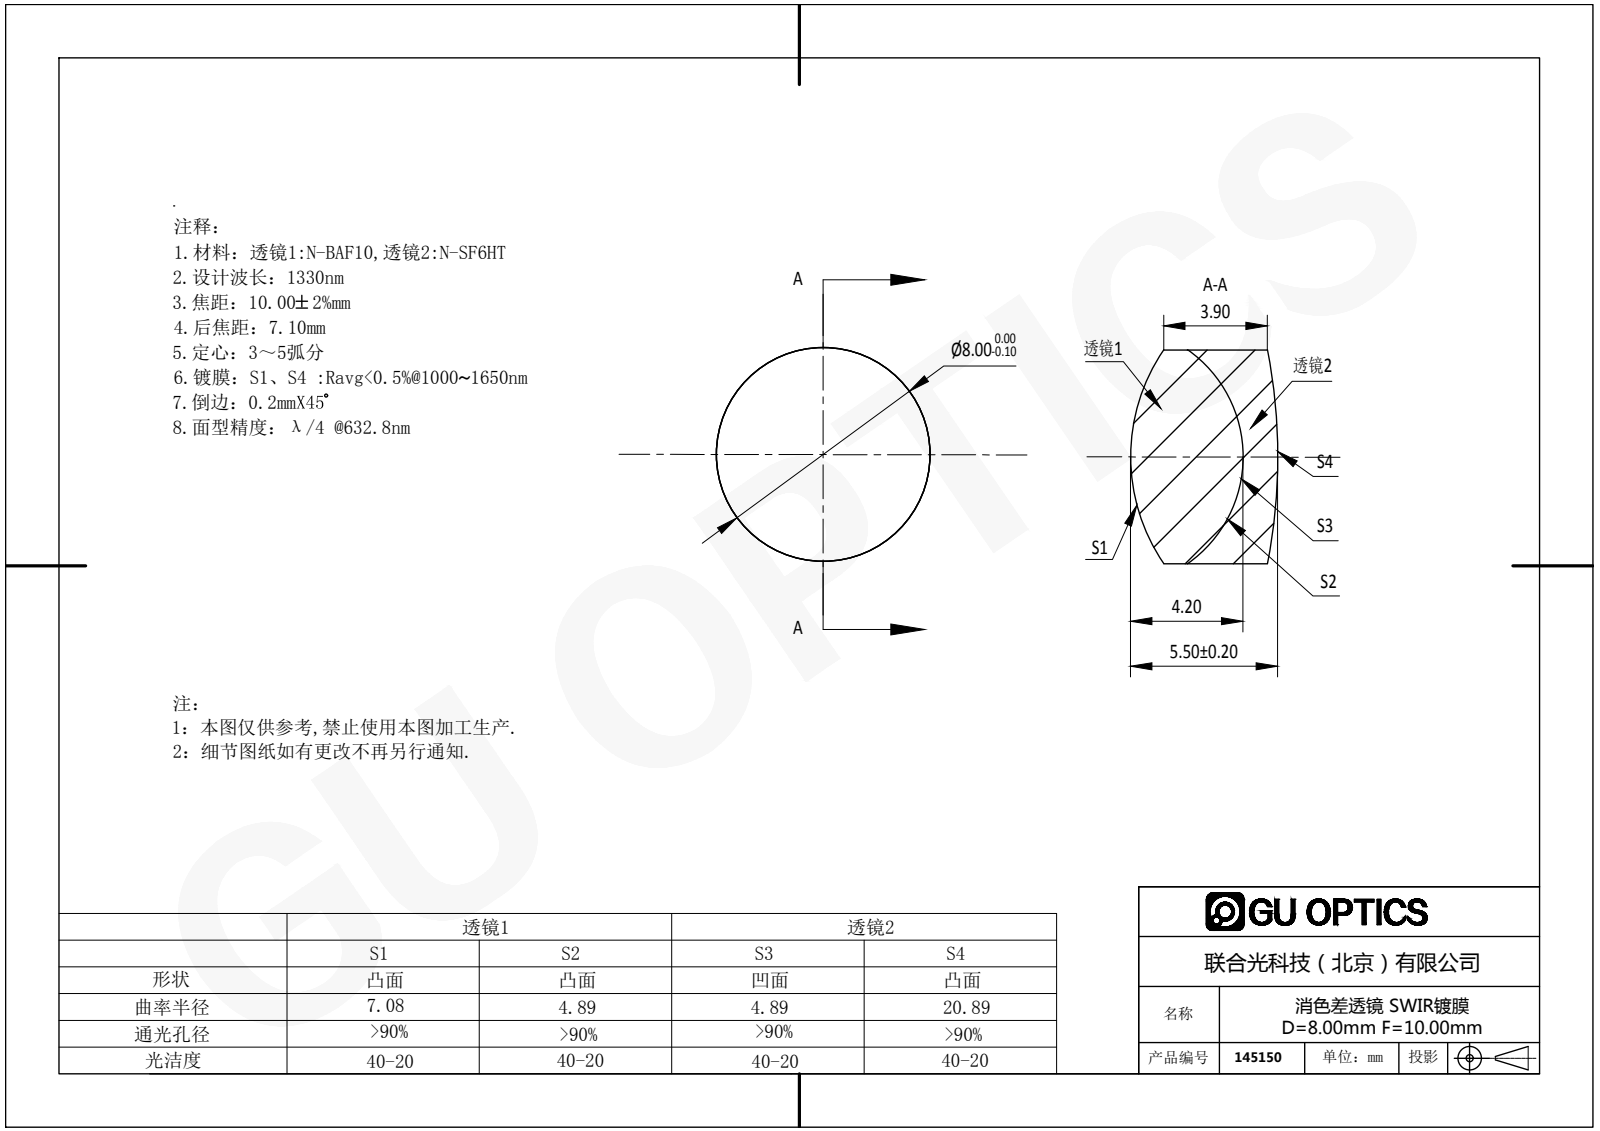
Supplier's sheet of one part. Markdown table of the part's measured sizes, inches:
| quantity | value |
| --- | --- |
| part name | 145150 |
| STEP written by | SolidWorks 2016 (AUTOMOTIVE_DESIGN) |
| units | inches |
| bodies | 2 solids, 12 faces (0 planar, 4 cylindrical, 8 other) |
| overall size | 0.315 × 0.315 × 0.217 |
| volume | 0.014 in³ |
| surface area | 0.513 in² |
| round bosses / shafts (diameter × count) | 0.315 × 1 |
